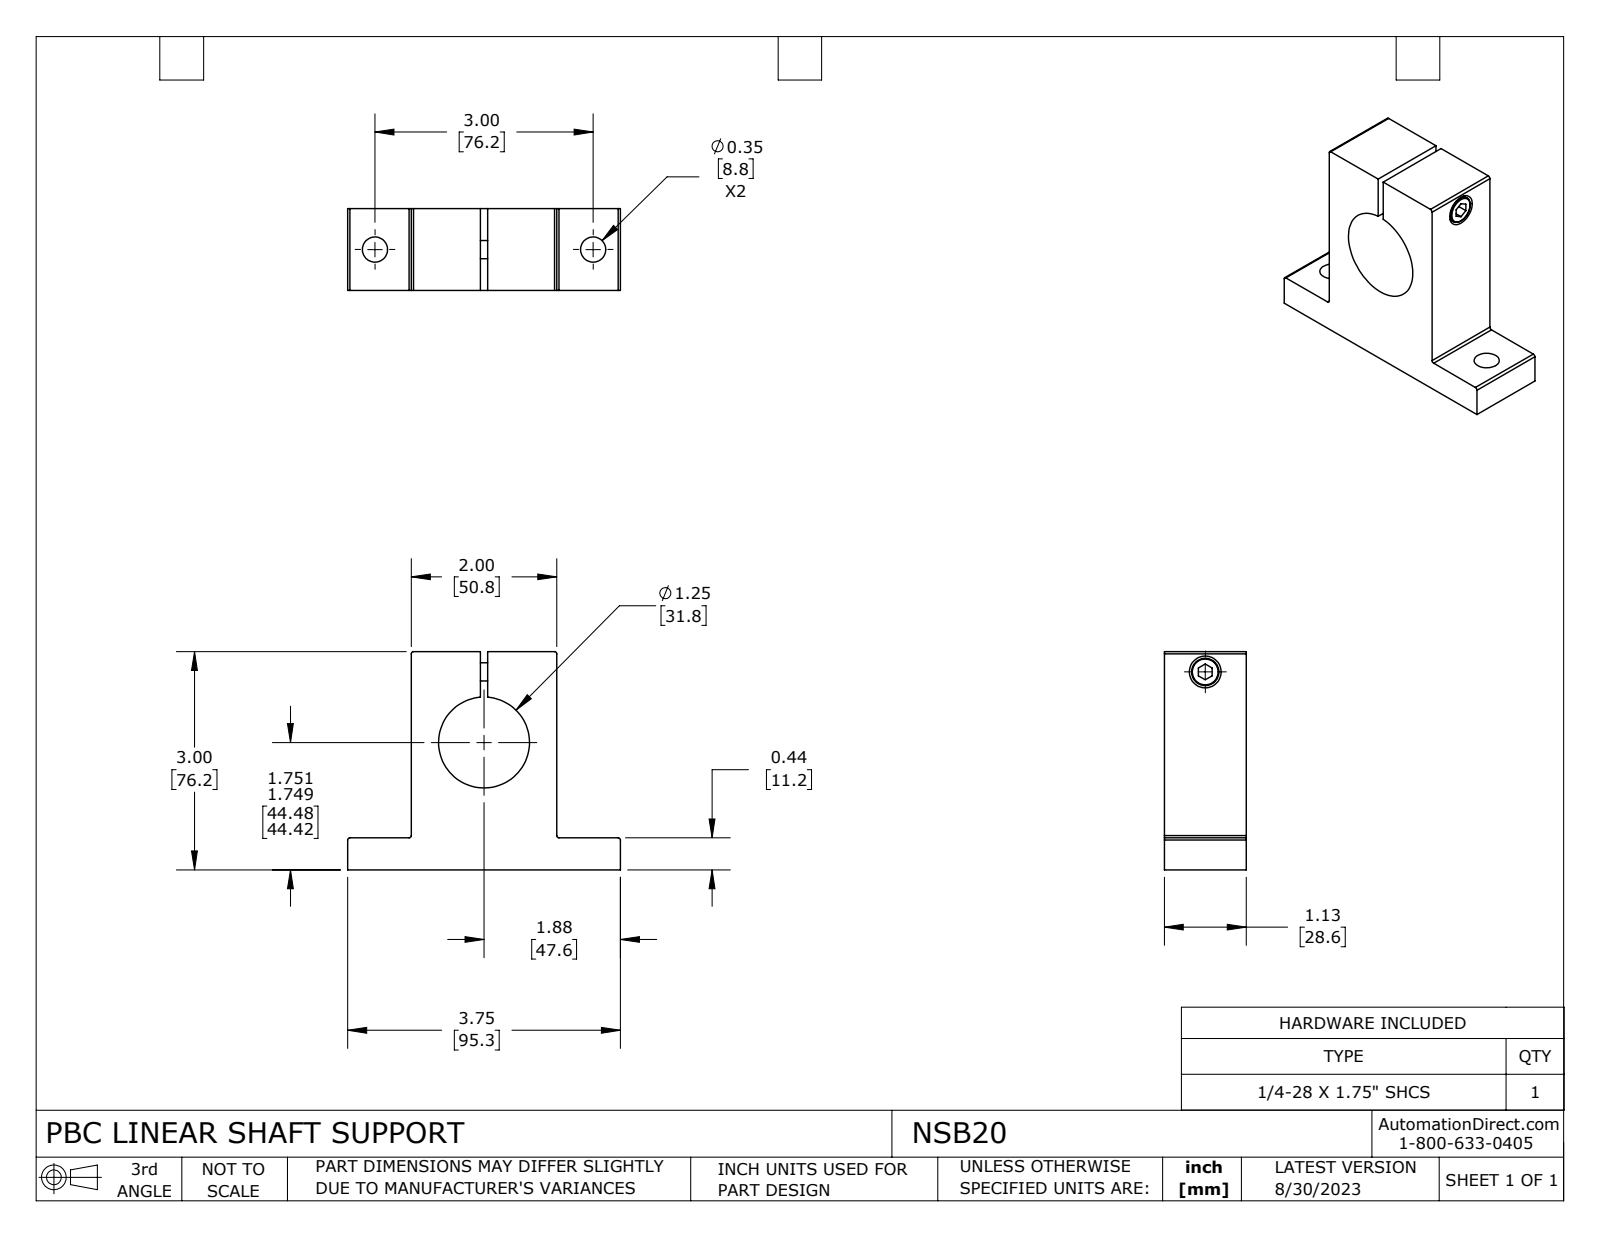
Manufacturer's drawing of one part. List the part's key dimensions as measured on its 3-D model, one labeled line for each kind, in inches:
Part name (STEP PRODUCT): NSB20
STEP written by: SolidWorks 2023 (CONFIG_CONTROL_DESIGN)
Units: inches
Bodies: 2 solids, 51 faces (24 planar, 23 cylindrical, 4 other)
Overall size (bounding box): 3.75 × 3 × 1.125
Volume: 6.082 in³ · Surface area: 35.61 in²
Round holes (diameter × count): ⌀0.346 ×2, ⌀0.213 ×1, ⌀0.266 ×1, ⌀0.437 ×1, ⌀1.25 ×1
Round bosses / shafts (diameter × count): ⌀0.375 ×1, ⌀0.25 ×1
Partial cylindrical surfaces — rounded edges, fillets, slot ends (radius × count): R0.031 ×6
Main face-to-face distances: 1.125, 2, 3, 0.44, 2.56, 0.951, 1.049, 0.875, 1.826, 1.924
Hole centre spacings: 3
